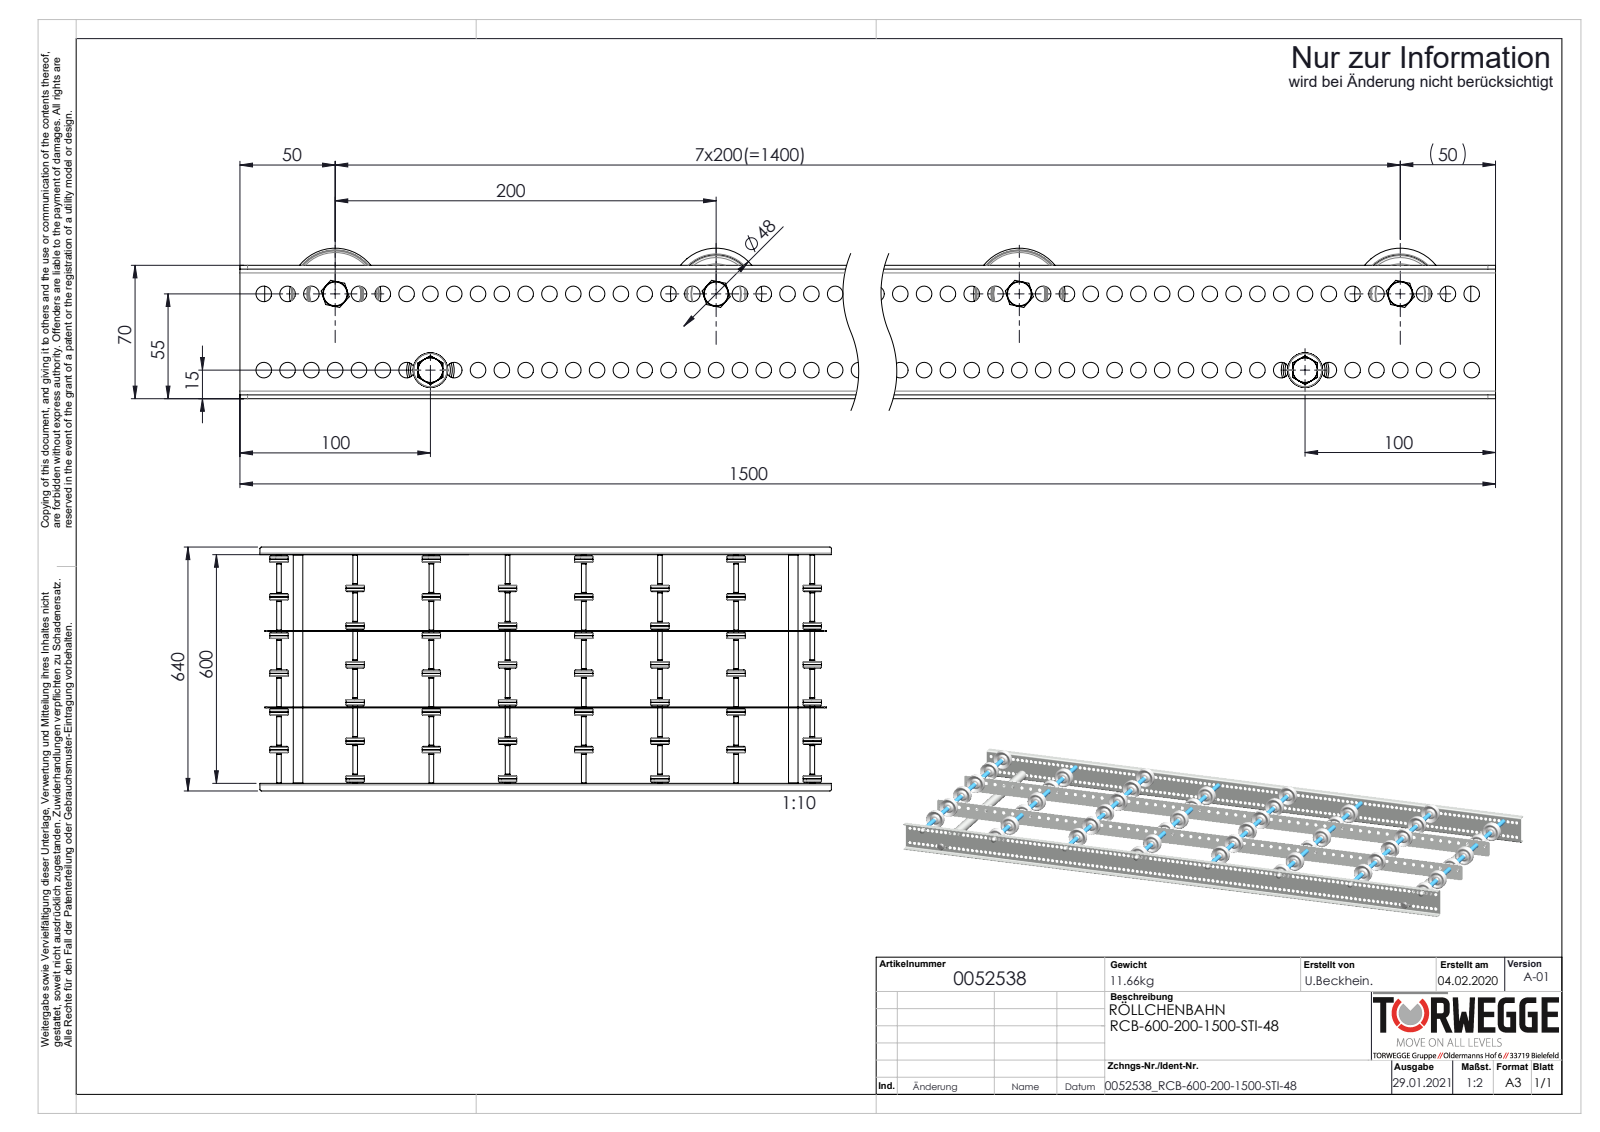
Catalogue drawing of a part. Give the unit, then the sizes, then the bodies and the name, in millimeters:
Units: millimetres
Overall size (bounding box): 1500 × 640 × 79
Round holes (diameter × count): ⌀8.2 ×238, ⌀8.5 ×59, ⌀6.65 ×8, ⌀8 ×8, ⌀9.65 ×8, ⌀15 ×8, ⌀41 ×8, ⌀6.8 ×2, ⌀21 ×2
Round bosses / shafts (diameter × count): ⌀48 ×8, ⌀13 ×8, ⌀12.5 ×8, ⌀12.4 ×8, ⌀12 ×8, ⌀11.5 ×8, ⌀25 ×2, ⌀8 ×2
Partial cylindrical surfaces — rounded edges, fillets, slot ends (radius × count): R4 ×8, R2 ×4, R5 ×4
Main face-to-face distances: 200.5, 2, 602, 2.5, 198, 401, 68, 99, 76, 604
Hole centre spacings: 12.5, 25, 37.5, 50, 62.5, 75, 87.5, 100
Volume: 2 479 000 mm³ · Surface area: 2 027 000 mm²
Bodies: 182 solids, 6128 faces (1140 planar, 2772 cylindrical, 2216 other)
Part name (STEP PRODUCT): S106837_Gewindestange-M8-KFG_L620; Profil_LRB-20x70x20x2_KFG_S100201_U-PROFIL-20-70-20-2-LRB-L=1500; Traversen_KFG_L600; 0052538 (+6 more)
STEP written by: SolidWorks 2020 (AUTOMOTIVE_DESIGN)
